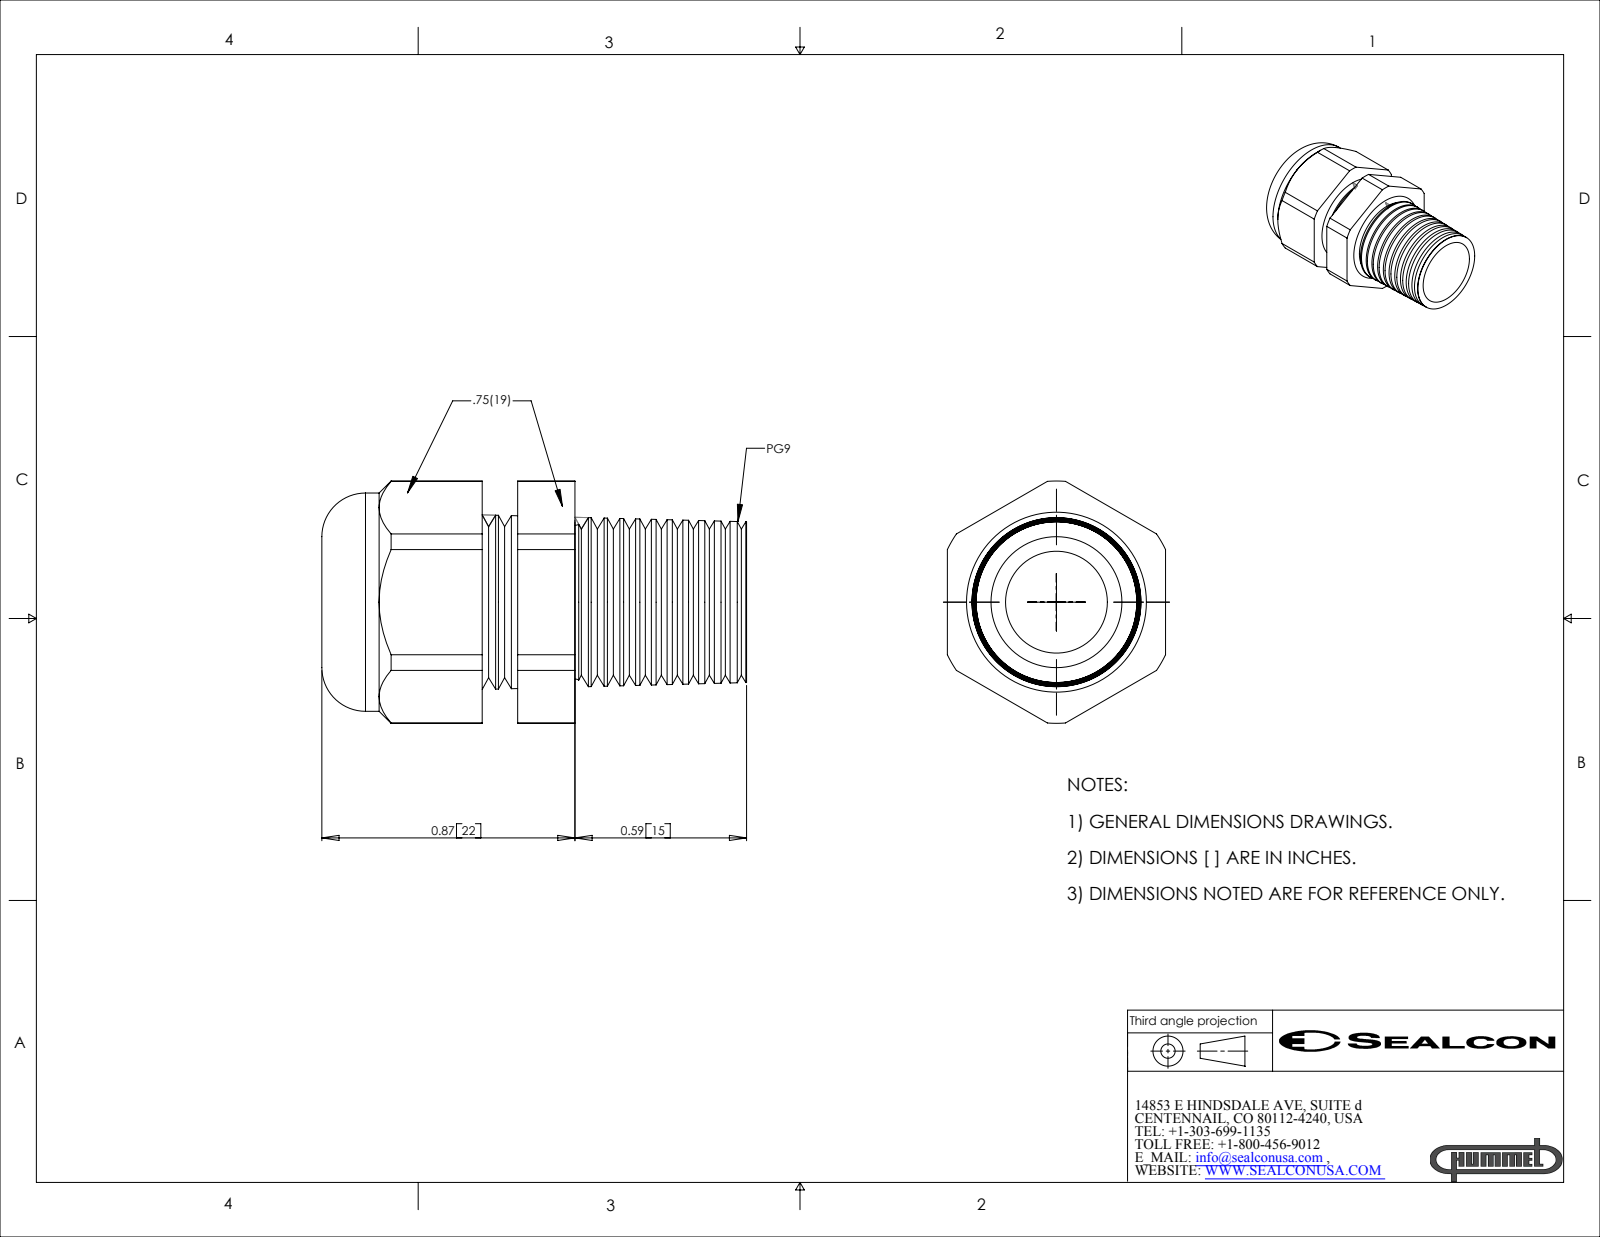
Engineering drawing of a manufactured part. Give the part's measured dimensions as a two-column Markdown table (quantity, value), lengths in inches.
| quantity | value |
| --- | --- |
| part name | CD09CA-BK |
| STEP written by | SolidWorks 2007 (CONFIG_CONTROL_DESIGN) |
| units | inches |
| bodies | 2 solids, 135 faces (19 planar, 22 cylindrical, 94 other) |
| overall size | 1.46 × 0.833 × 0.75 |
| volume | 0.34 in³ |
| surface area | 7.272 in² |
| round holes (diameter × count) | 0.35 × 1, 0.45 × 1 |
| round bosses / shafts (diameter × count) | 0.75 × 1 |
| partial cylindrical surfaces (radius × count) | 0.416 × 1 |
| main face-to-face distances | 0.75, 0.122, 0.75, 0.319, 0.197, 0.354, 0.476, 0.673, 1.263, 0.909 |
